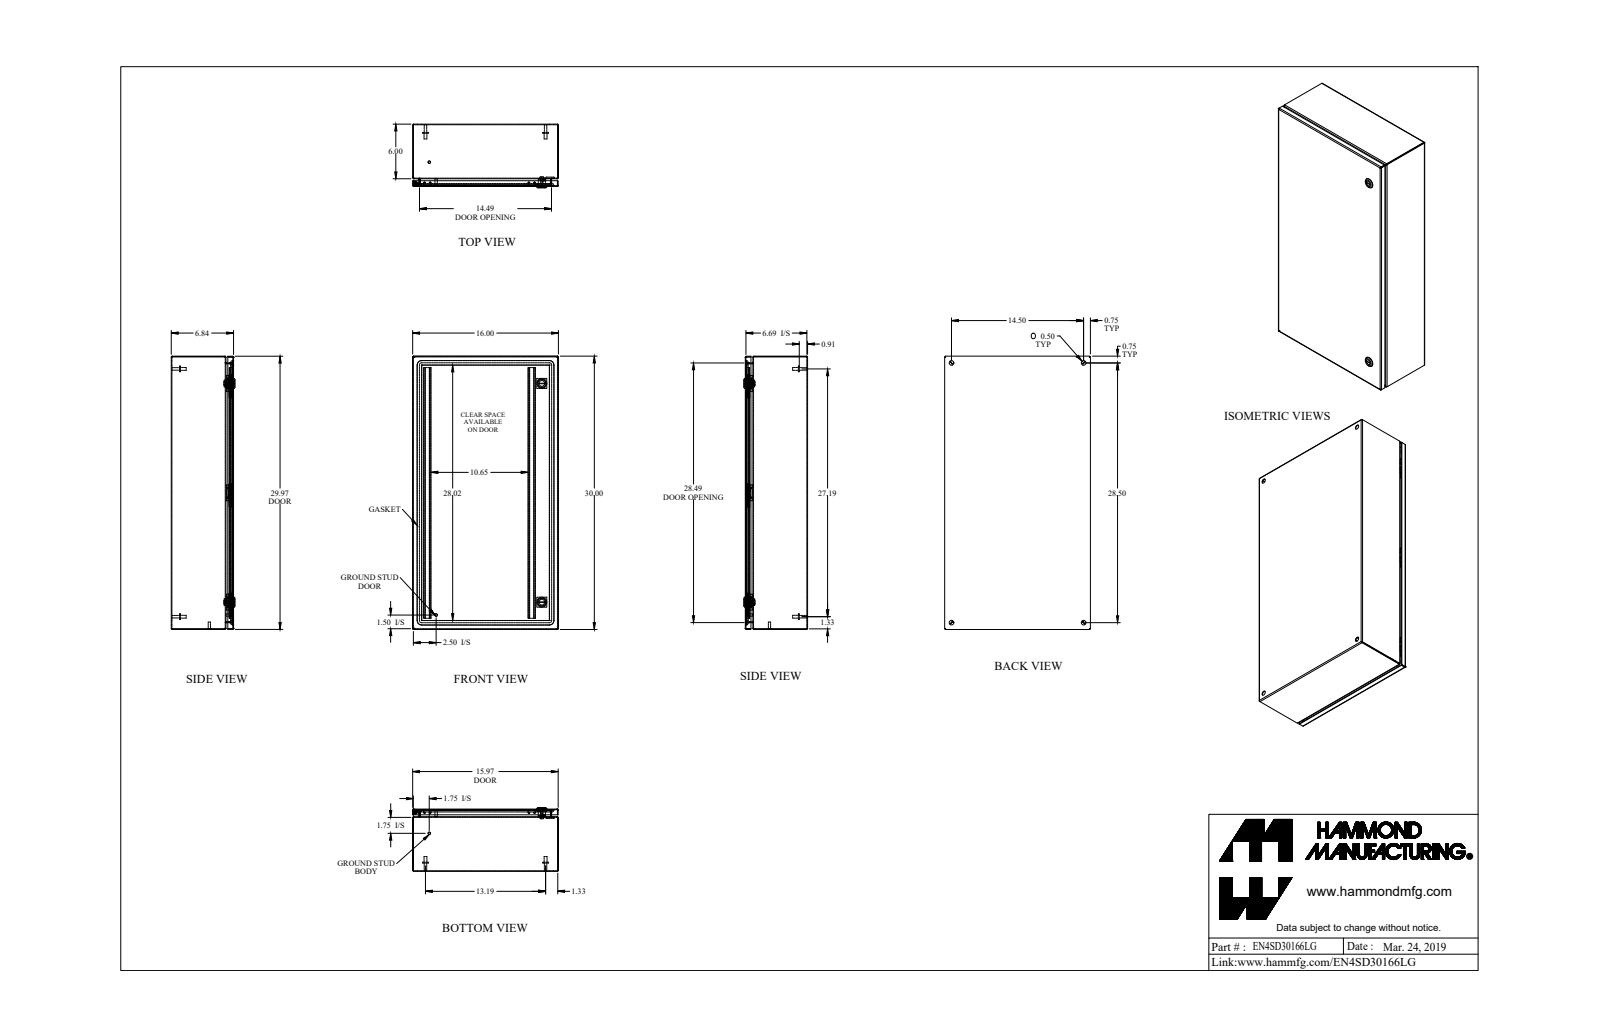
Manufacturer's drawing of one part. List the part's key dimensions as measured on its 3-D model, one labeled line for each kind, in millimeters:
Part name (STEP PRODUCT): EN4SD30166LG_Default
STEP written by: SolidWorks 2019 (CONFIG_CONTROL_DESIGN)
Units: millimetres
Bodies: 31 solids, 885 faces (422 planar, 295 cylindrical, 168 other)
Overall size (bounding box): 762 × 406.4 × 177.7
Volume: 2 211 000 mm³ · Surface area: 2 455 000 mm²
Round holes (diameter × count): ⌀12.7 ×4, ⌀5.9 ×2, ⌀15.9 ×2, ⌀19.9 ×2, ⌀4.4 ×1, ⌀6.1 ×1, ⌀6.1 ×1
Round bosses / shafts (diameter × count): ⌀15.9 ×4, ⌀8 ×4, ⌀6.9 ×4, ⌀27.9 ×2, ⌀13.3 ×2, ⌀7.1 ×2, ⌀6.4 ×2, ⌀11.6 ×1
Partial cylindrical surfaces — rounded edges, fillets, slot ends (radius × count): R0.9 ×20, R2.7 ×20, R1.1 ×12, R2.1 ×12, R9.7 ×12, R482.7 ×8, R0.2 ×6, R1.6 ×6
Main face-to-face distances: 1.8, 171.8, 170, 173.7, 404.6, 760.2, 402.7, 406.4, 21.3, 150.6
Hole centre spacings: 345.8, 368.3, 723.9, 812.2, 63.3, 63.3, 609.6, 667.3
